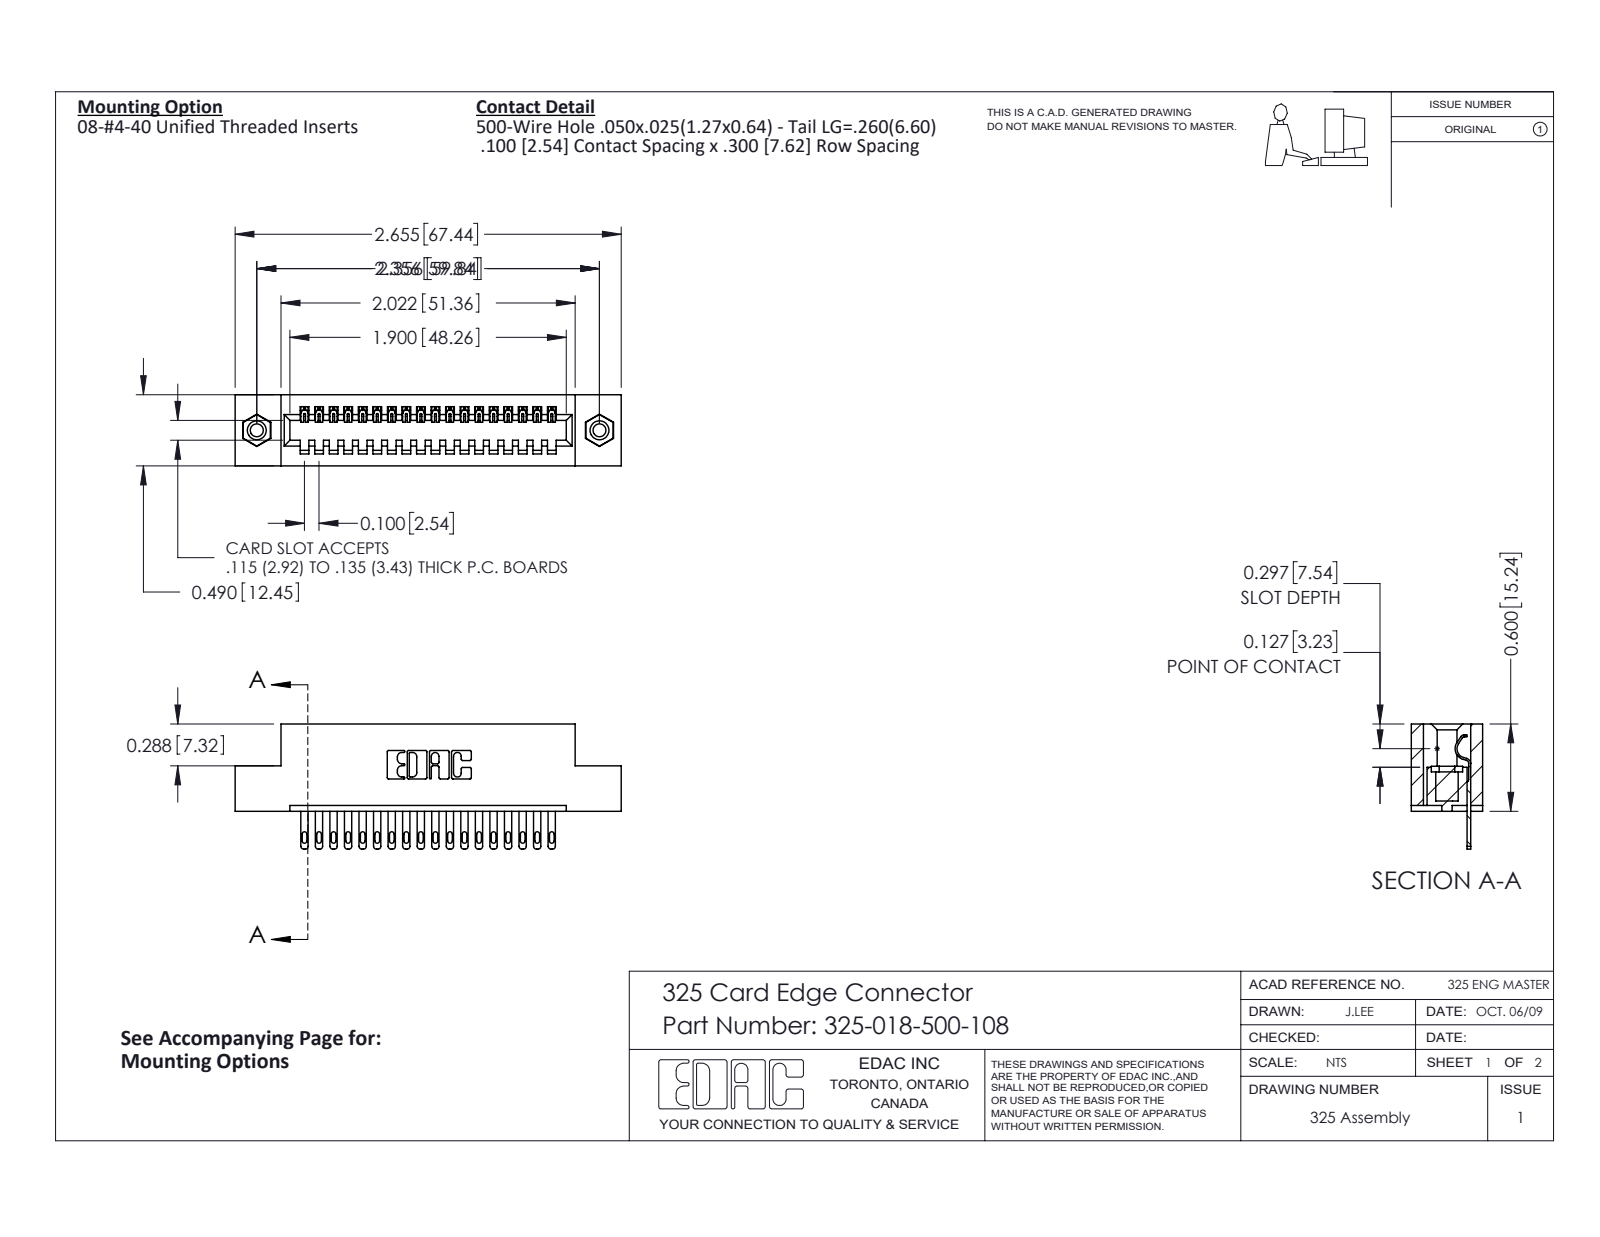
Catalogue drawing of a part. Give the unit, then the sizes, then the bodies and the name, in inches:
Units: inches
Overall size (bounding box): 2.655 × 0.86 × 0.49
Round holes (diameter × count): ⌀0.089 ×2, ⌀0.125 ×2, ⌀0.16 ×2
Round bosses / shafts (diameter × count): ⌀0.155 ×2
Partial cylindrical surfaces — rounded edges, fillets, slot ends (radius × count): R0.006 ×36, R0.016 ×36, R0.02 ×36, R0.01 ×22, R0.007 ×6, R0.031 ×6, R0.026 ×3, R0.014 ×1
Main face-to-face distances: 0.083, 0.407, 0.3, 0.49, 0.107, 0.383, 0.025, 0.6, 0.2, 0.04
Hole centre spacings: 2.356
Volume: 0.511 in³ · Surface area: 13.64 in²
Bodies: 21 solids, 1146 faces (750 planar, 380 cylindrical, 16 other)
Part name (STEP PRODUCT): 325 Part_TI; 345-250-001_345-250-003-102; 325-018-500-108; 325-292-001_325-293-100
STEP written by: SolidWorks 2016 (CONFIG_CONTROL_DESIGN)
